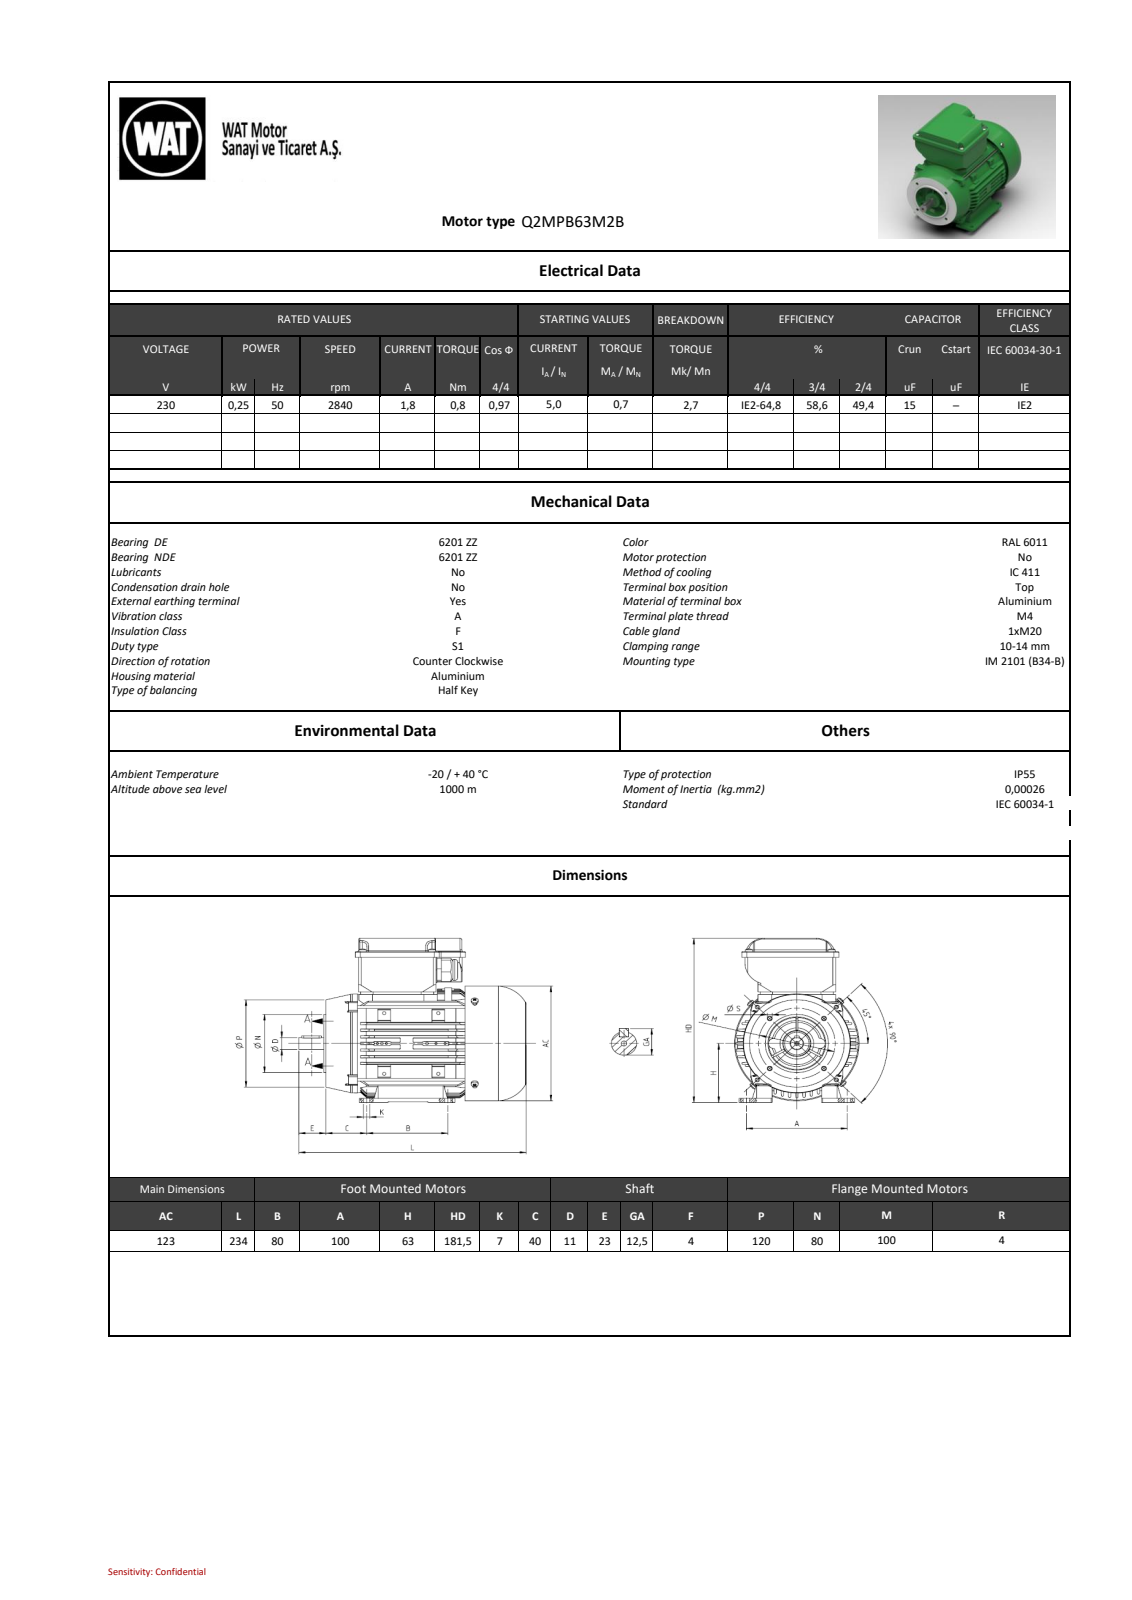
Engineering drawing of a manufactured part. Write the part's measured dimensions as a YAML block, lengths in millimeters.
part_name: "BY6434017xx_004-TK_QM63-80; BY6424130xx_004-TKK_QM63-80; BY6424189xx_005-MOTOR_KAPAGI_QS63FB_ISLEME; BY6423003xx_006-FAN_KAPAGI_QS63 (+8 more)"
step_written_by: "SIEMENS PLM Software NX2206.8101 (AUTOMOTIVE_DESIGN)"
units: millimeters
bodies: {solids: 36, faces: 2420, planar: 1185, cylindrical: 814, other: 421}
overall_size: [233.47, 181.5, 123]
volume: 663584
surface_area: 436829
round_holes:
  - {diameter: 3.65, count: 10}
  - {diameter: 4, count: 8}
  - {diameter: 4.5, count: 8}
  - {diameter: 2.5, count: 6}
  - {diameter: 3.3, count: 5}
  - {diameter: 4.2, count: 4}
  - {diameter: 4.65, count: 4}
  - {diameter: 4.8, count: 4}
  - {diameter: 6, count: 4}
  - {diameter: 3, count: 3}
  - {diameter: 7, count: 2}
  - {diameter: 5, count: 1}
round_bosses_or_shafts:
  - {diameter: 8, count: 8}
  - {diameter: 4, count: 8}
  - {diameter: 3, count: 8}
  - {diameter: 4.8, count: 4}
  - {diameter: 123, count: 1}
  - {diameter: 120, count: 1}
  - {diameter: 80, count: 1}
  - {diameter: 25.28, count: 1}
partial_cylinders:
  - {radius: 0.5, count: 212}
  - {radius: 1, count: 121}
  - {radius: 2, count: 69}
  - {radius: 5, count: 26}
  - {radius: 3, count: 21}
  - {radius: 2.5, count: 20}
  - {radius: 5.5, count: 9}
  - {radius: 1.5, count: 8}
face_to_face_distances: [3, 1, 4.5, 181.5, 7.02, 27.96, 4, 1.5, 147.5, 28.05]
hole_center_spacings: [55, 54, 0.61, 54.58, 62.8, 63, 66.91, 70.71]
